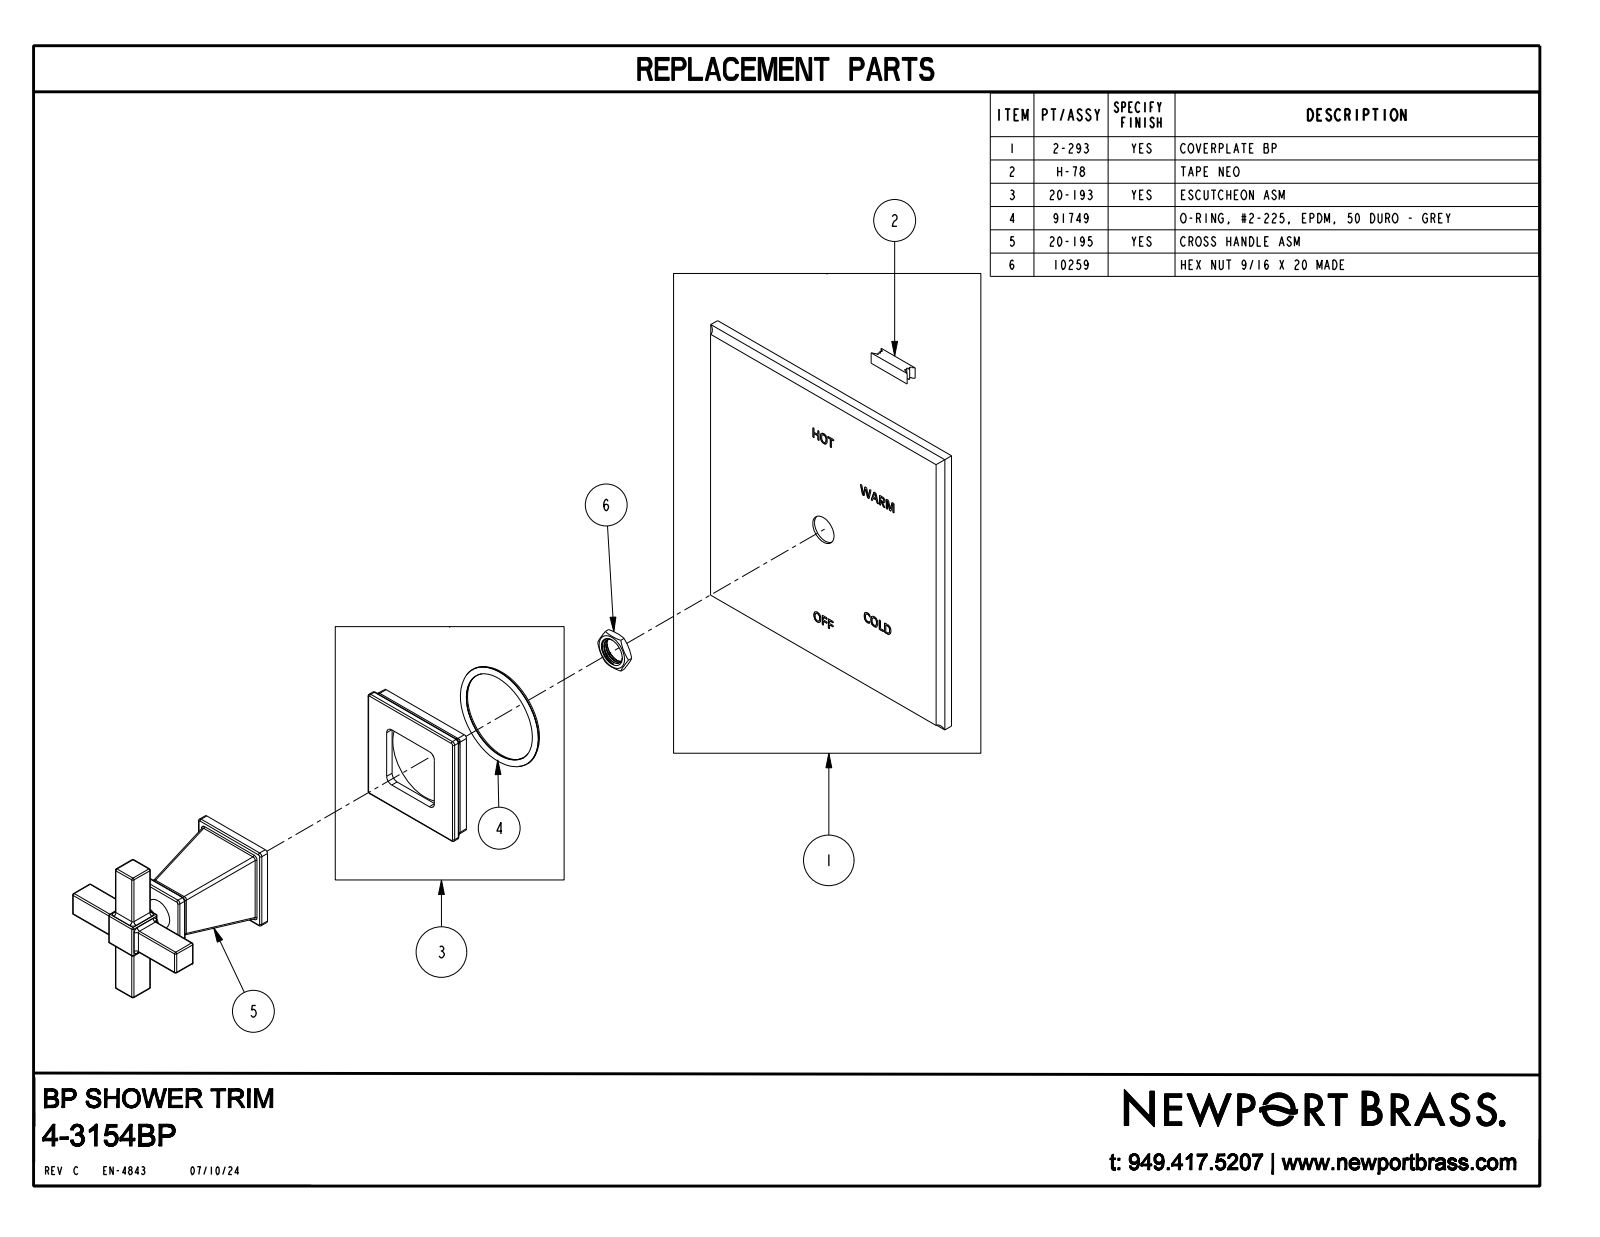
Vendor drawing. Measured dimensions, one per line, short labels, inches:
name: 4-3154BP
written by: CREO PARAMETRIC BY PTC INC, 2018400 (CONFIG_CONTROL_DESIGN)
unit: in
bodies: 1 solid, 505 faces (185 planar, 128 cylindrical, 192 other)
size: 6.5 × 6.5 × 3.941
volume: 20.03 in³; area: 117.8 in²
bosses: 1× ⌀0.625, 1× ⌀0.506
rounds: 60× R0.03, 36× R0.06, 8× R0.09, 4× R0.125, 4× R0.23
face distances: 0.313, 0.5, 3, 3.5, 0.723, 0.41, 6.5, 3.348, 3.848, 3.035
